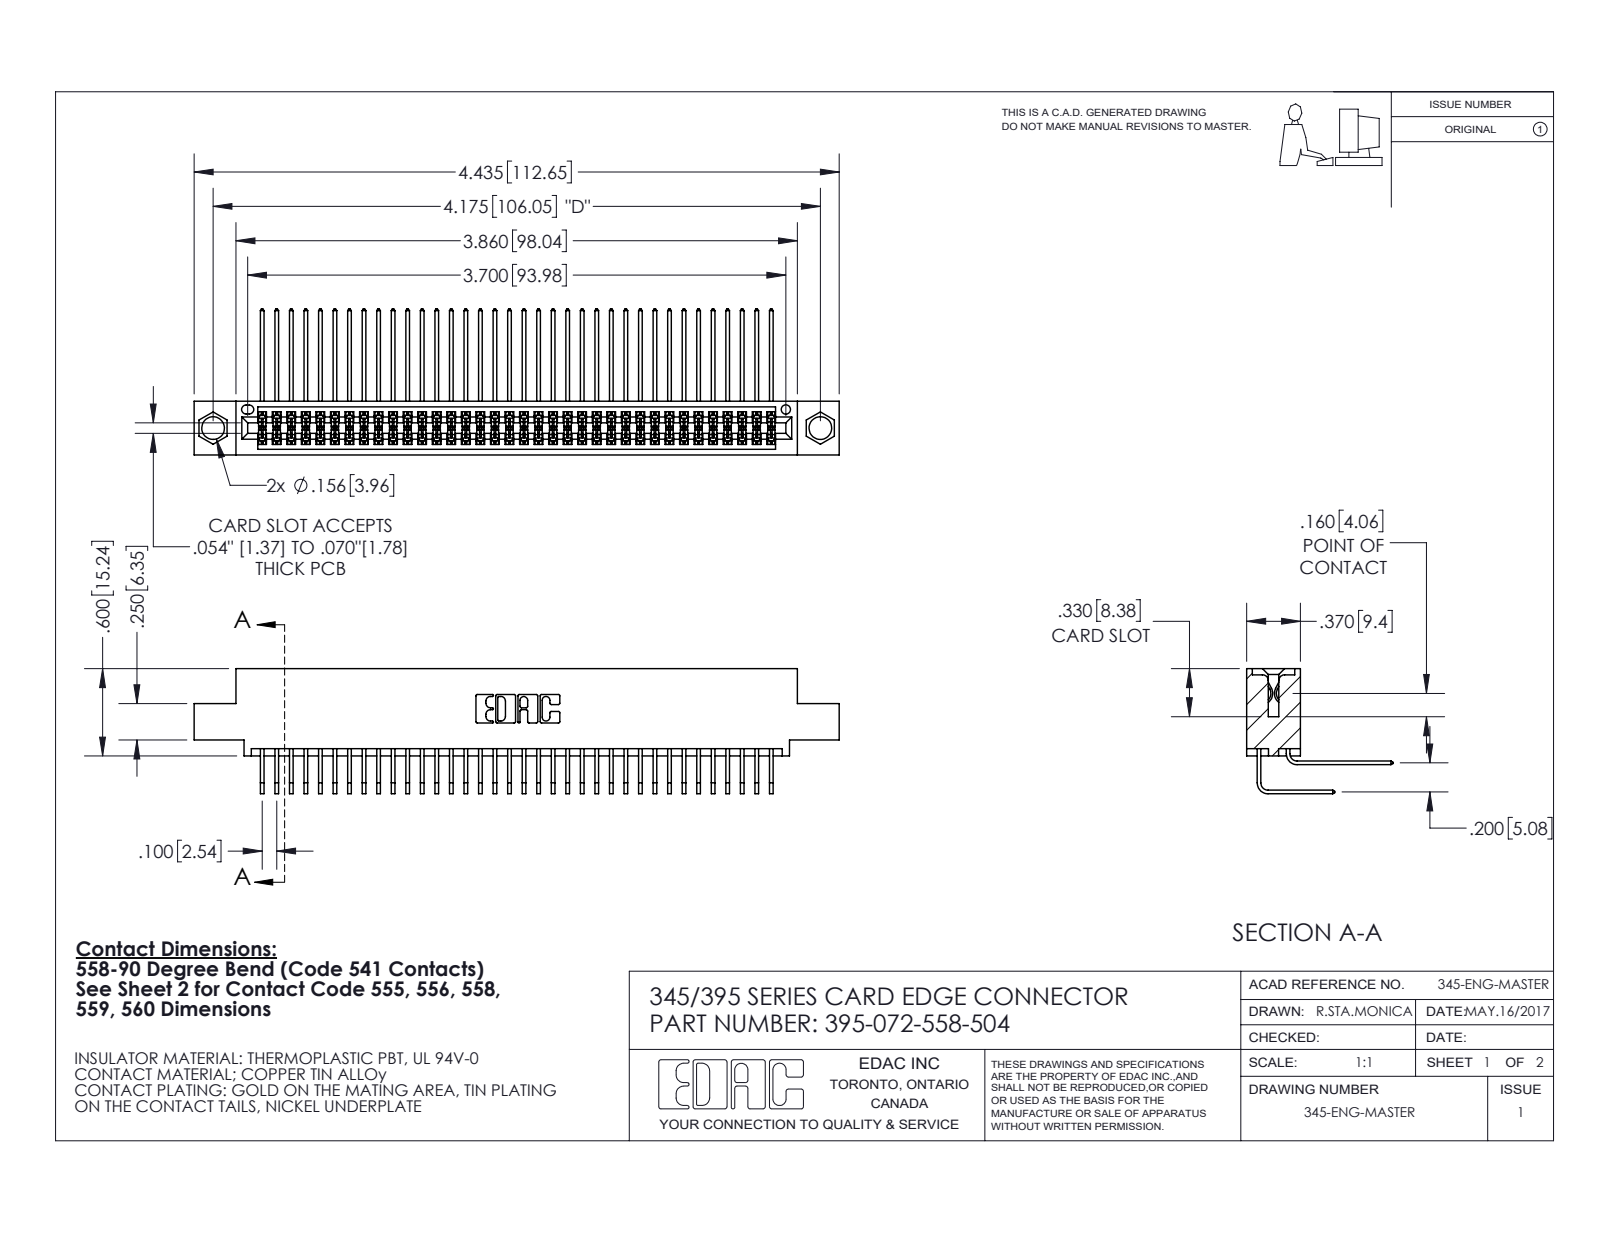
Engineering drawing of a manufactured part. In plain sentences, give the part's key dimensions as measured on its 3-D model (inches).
The part is named "345-292-001_558 Tail - 2; 345-292-001_558 559 Tail - 1; 395-072-558-504; 345 Part_0.110 Offset - 0.156 Dia-TI". Its 3-D file was written by "SolidWorks 2020 (CONFIG_CONTROL_DESIGN)". It is 73 solids with 3888 faces: 2618 planar, 1270 cylindrical and 0 other. Overall it measures 4.435 by 1.005 by 0.859 inches. Its volume is 0.679 cubic inches and its surface area 28.25 square inches. Round holes: 2 of diameter 0.156, 1 of diameter 0.064. Partial cylindrical surfaces (rounded edges, fillets, slot ends): 108 of radius 0.006, 22 of radius 0.01, 6 of radius 0.007, 6 of radius 0.031, 3 of radius 0.026, 2 of radius 0.014, 2 of radius 0.019, 2 of radius 0.022. The main face-to-face distances are 0.072, 0.298, 0.2, 0.37, 0.098, 0.272, 0.025, 0.225, 0.025, 0.175. The hole center spacings are 0.27, 3.939, 4.175.
